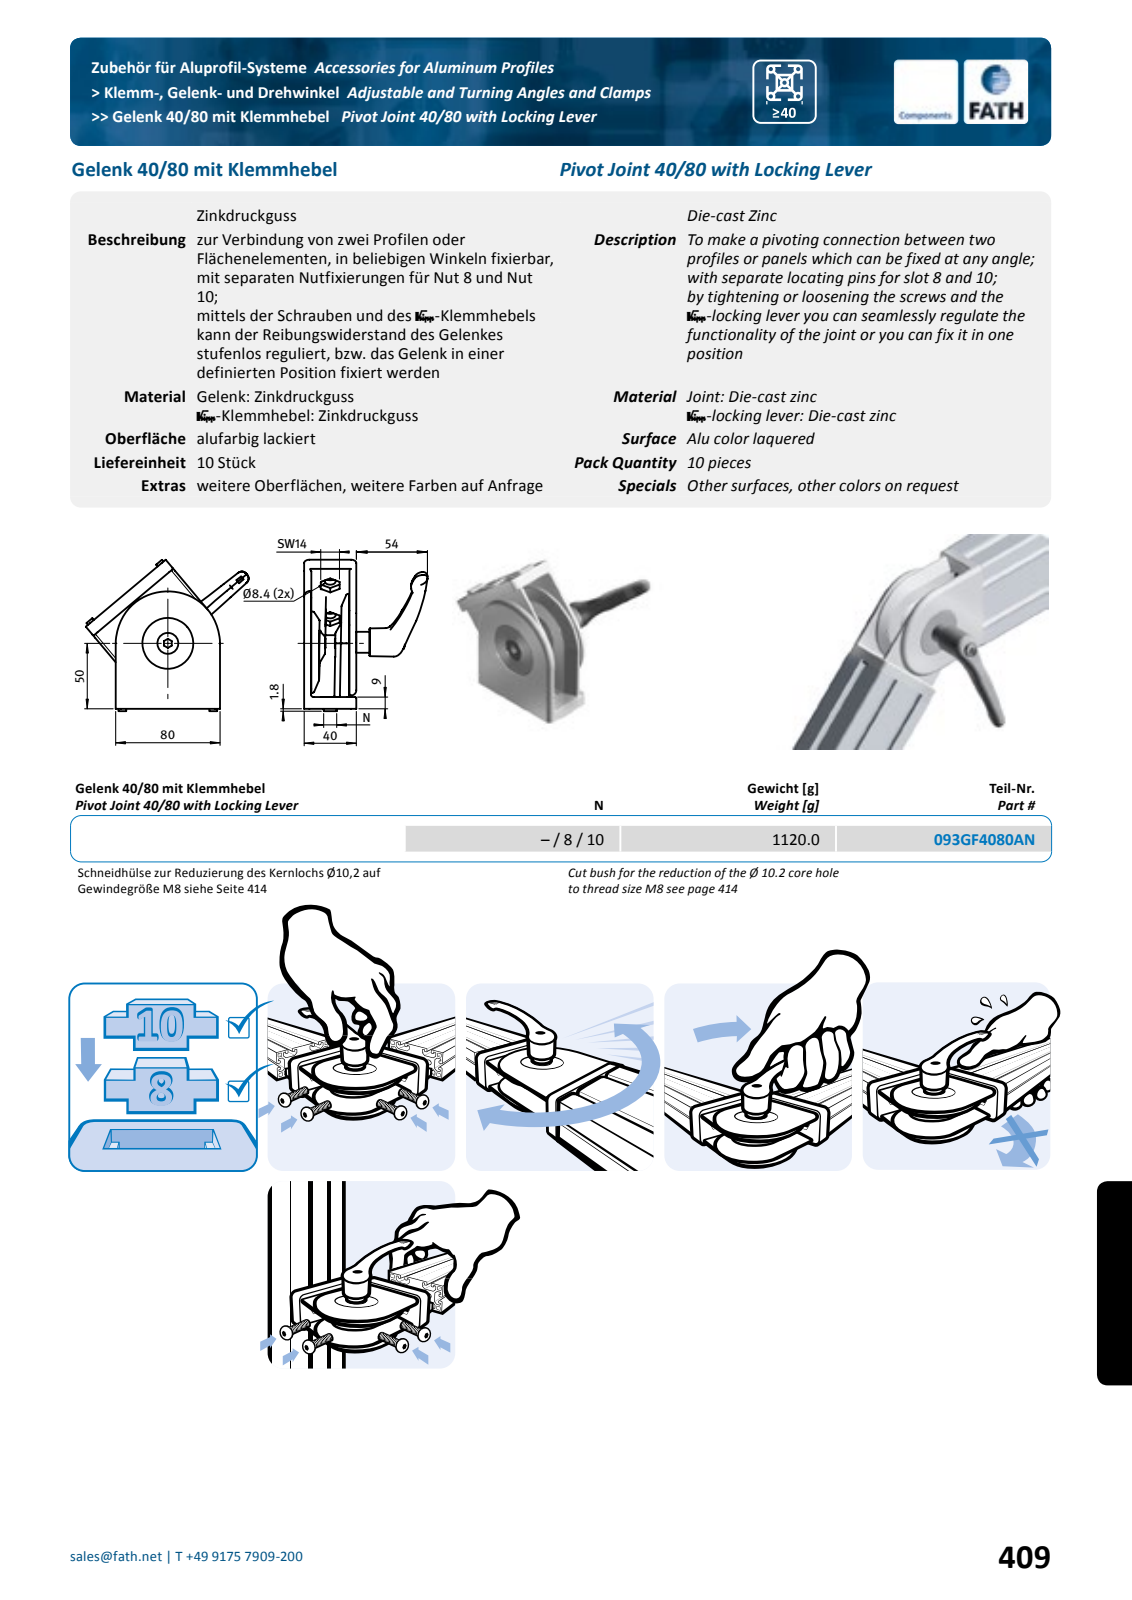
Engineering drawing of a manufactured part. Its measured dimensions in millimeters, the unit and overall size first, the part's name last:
Units: millimetres
Overall size (bounding box): 113.89 × 102.43 × 80.69
Round holes (diameter × count): ⌀6.8 ×1, ⌀8.2 ×1, ⌀8.3 ×1, ⌀9 ×1, ⌀14 ×1, ⌀20 ×1, ⌀60.4 ×1, ⌀70 ×1
Round bosses / shafts (diameter × count): ⌀2 ×4, ⌀79.6 ×1, ⌀75.6 ×1, ⌀69.6 ×1, ⌀60 ×1, ⌀40 ×1, ⌀28 ×1, ⌀16 ×1
Partial cylindrical surfaces — rounded edges, fillets, slot ends (radius × count): R1 ×44, R2 ×39, R0.5 ×24, R4 ×8, R0.4 ×6, R0.3 ×4, R1.5 ×4, R2.5 ×4
Main face-to-face distances: 5.2, 34.6, 39.8, 29.4, 34.3, 5.5, 29.1, 34.5, 28.8, 1
Volume: 182 933 mm³ · Surface area: 85 194 mm²
Bodies: 9 solids, 1070 faces (251 planar, 249 cylindrical, 570 other)
Part name (STEP PRODUCT): fath_093gf4080an_1; fath_093gf4080an_2; fath_093gf4080an_3; fath_093gf4080an_4 (+5 more)
STEP written by: Spatial InterOp 3D (automotive_design)
